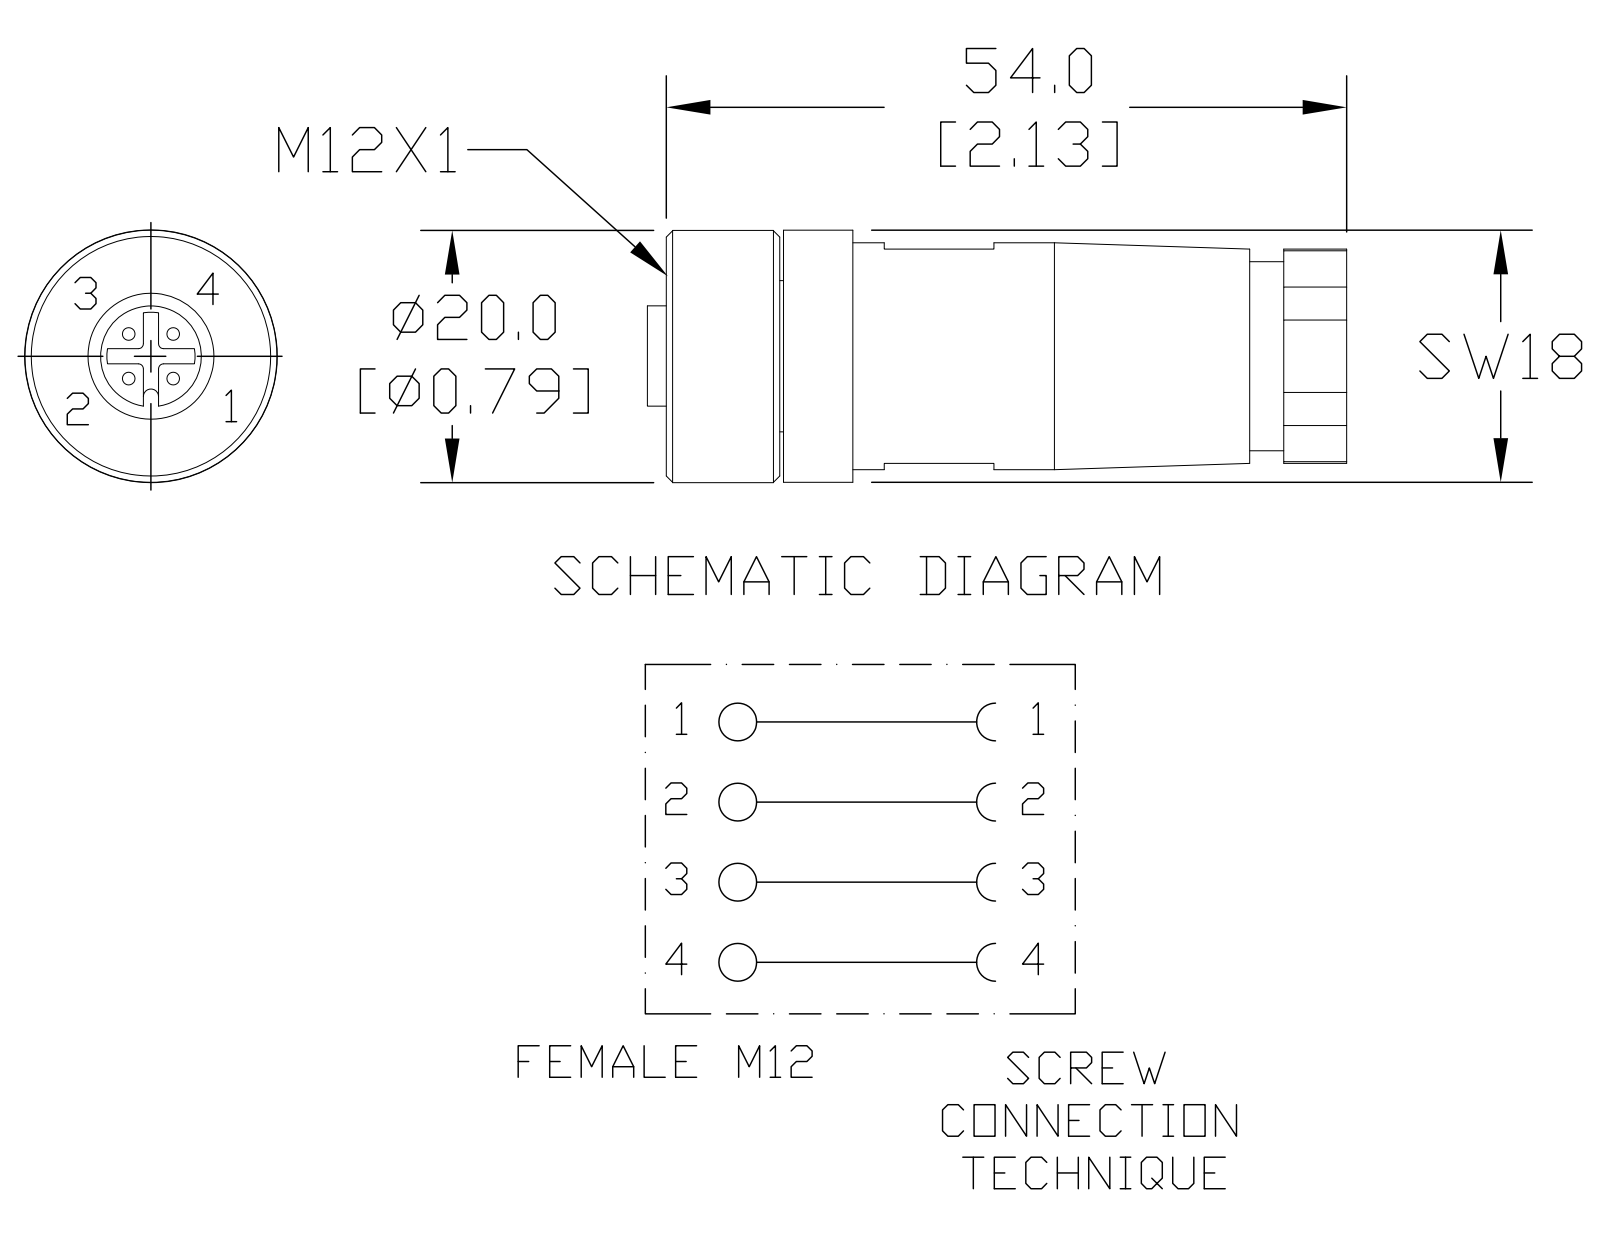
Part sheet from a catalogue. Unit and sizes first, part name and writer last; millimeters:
Units: millimetres
Overall size (bounding box): 54 × 20 × 19.99
Round holes (diameter × count): ⌀1 ×4, ⌀6.98 ×1, ⌀9.12 ×1
Round bosses / shafts (diameter × count): ⌀17.78 ×1, ⌀11.07 ×1, ⌀7.99 ×1
Partial cylindrical surfaces — rounded edges, fillets, slot ends (radius × count): R10 ×1
Main face-to-face distances: 11.07, 2.25, 14.25, 12, 1.2, 6.32, 7.52, 11, 41.93, 42
Hole centre spacings: 3.3, 3.32, 4.68, 2.22, 2.34, 2.35, 2.46
Volume: 11 359 mm³ · Surface area: 5 586 mm²
Bodies: 1 solid, 786 faces (408 planar, 194 cylindrical, 184 other)
Part name (STEP PRODUCT): 7000-12901-0000000
STEP written by: SolidWorks 2015 (AUTOMOTIVE_DESIGN)
